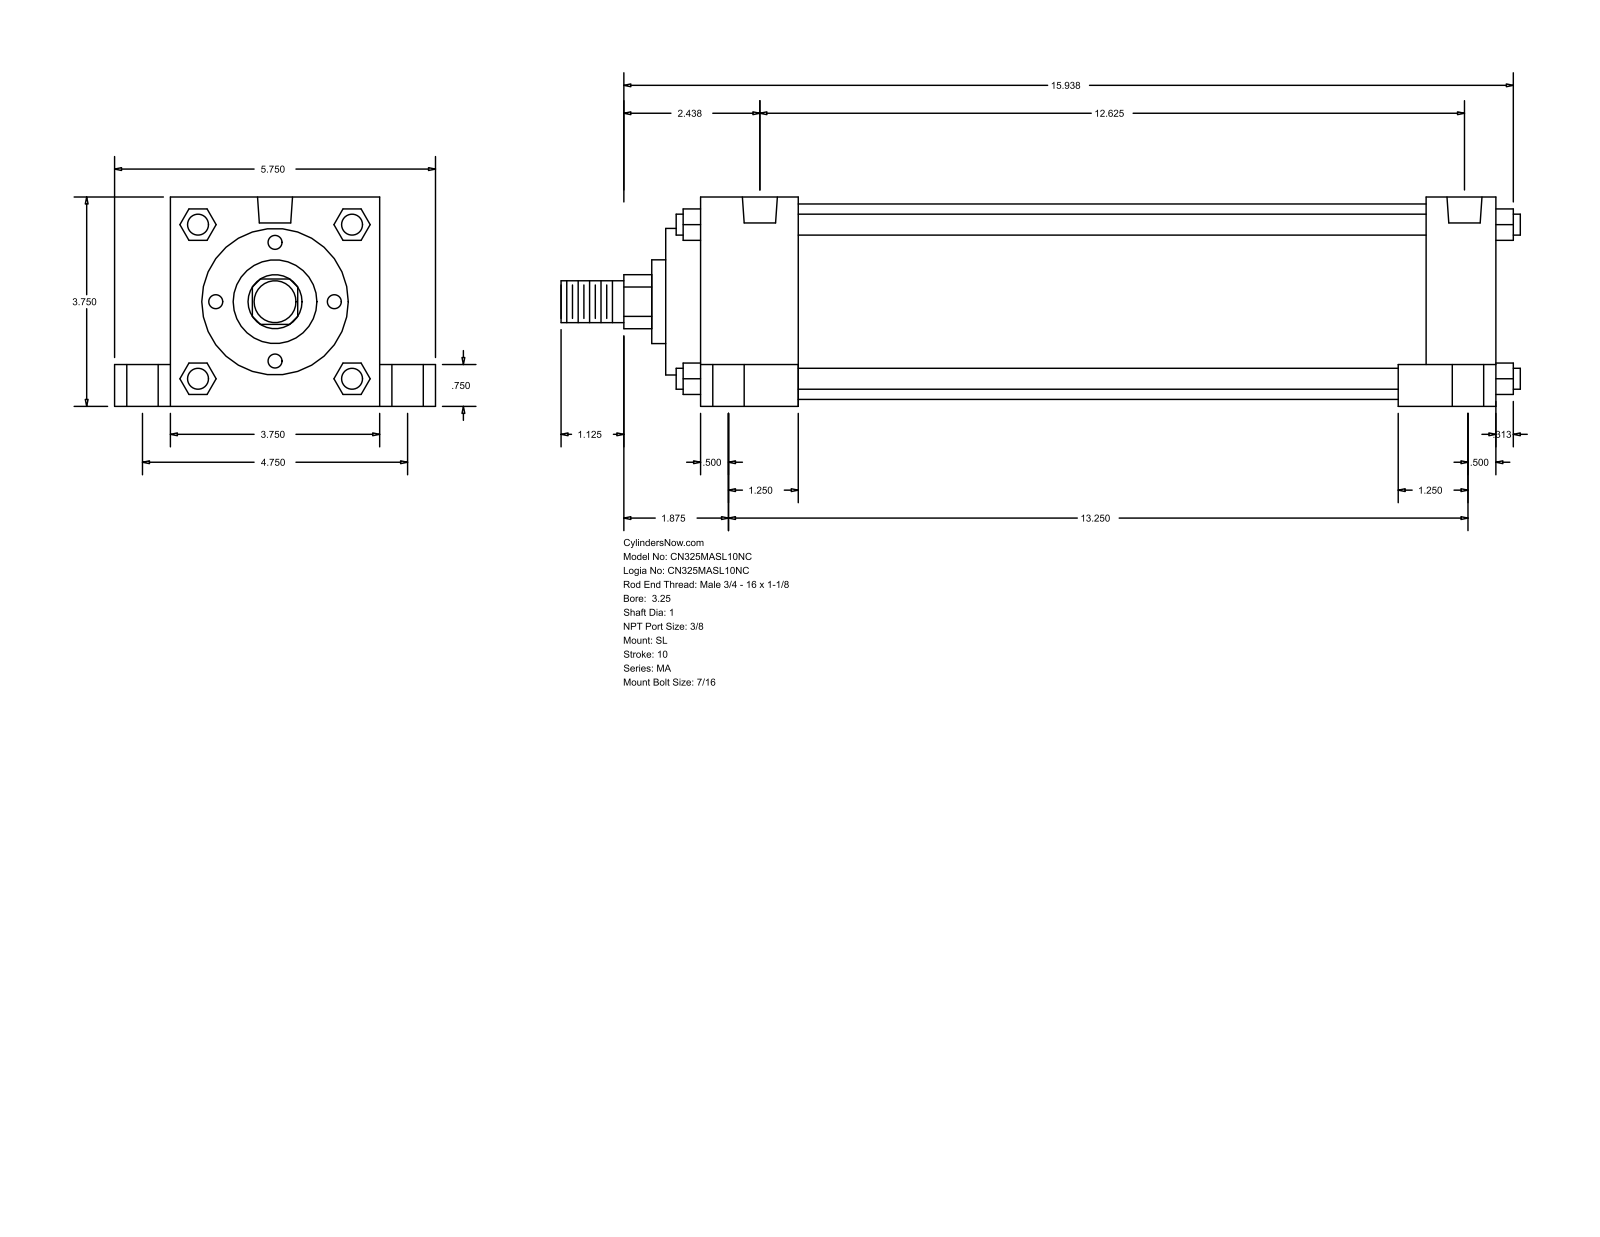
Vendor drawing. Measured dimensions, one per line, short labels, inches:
name: MA_SL__0325_1
written by: GSSL Pune (CONFIG_CONTROL_DESIGN)
unit: in
bodies: 0 solids, 150 faces (113 planar, 37 cylindrical, 0 other)
size: 17.187 × 5.75 × 3.75
holes: 4× ⌀0.437, 4× ⌀0.563, 4× ⌀0.813, 2× ⌀0.627
bosses: 4× ⌀0.375, 1× ⌀3.5, 1× ⌀2.625, 1× ⌀1.5, 1× ⌀1, 1× ⌀0.75
rounds: 1× R0.484
face distances: 3.75, 14.25, 0.625, 1, 4.75, 0.75, 13, 1.25, 1.75, 11.25
hole spacings: 2.376, 2.388, 2.441, 2.491, 4.75, 12.25, 12.724, 12.908
